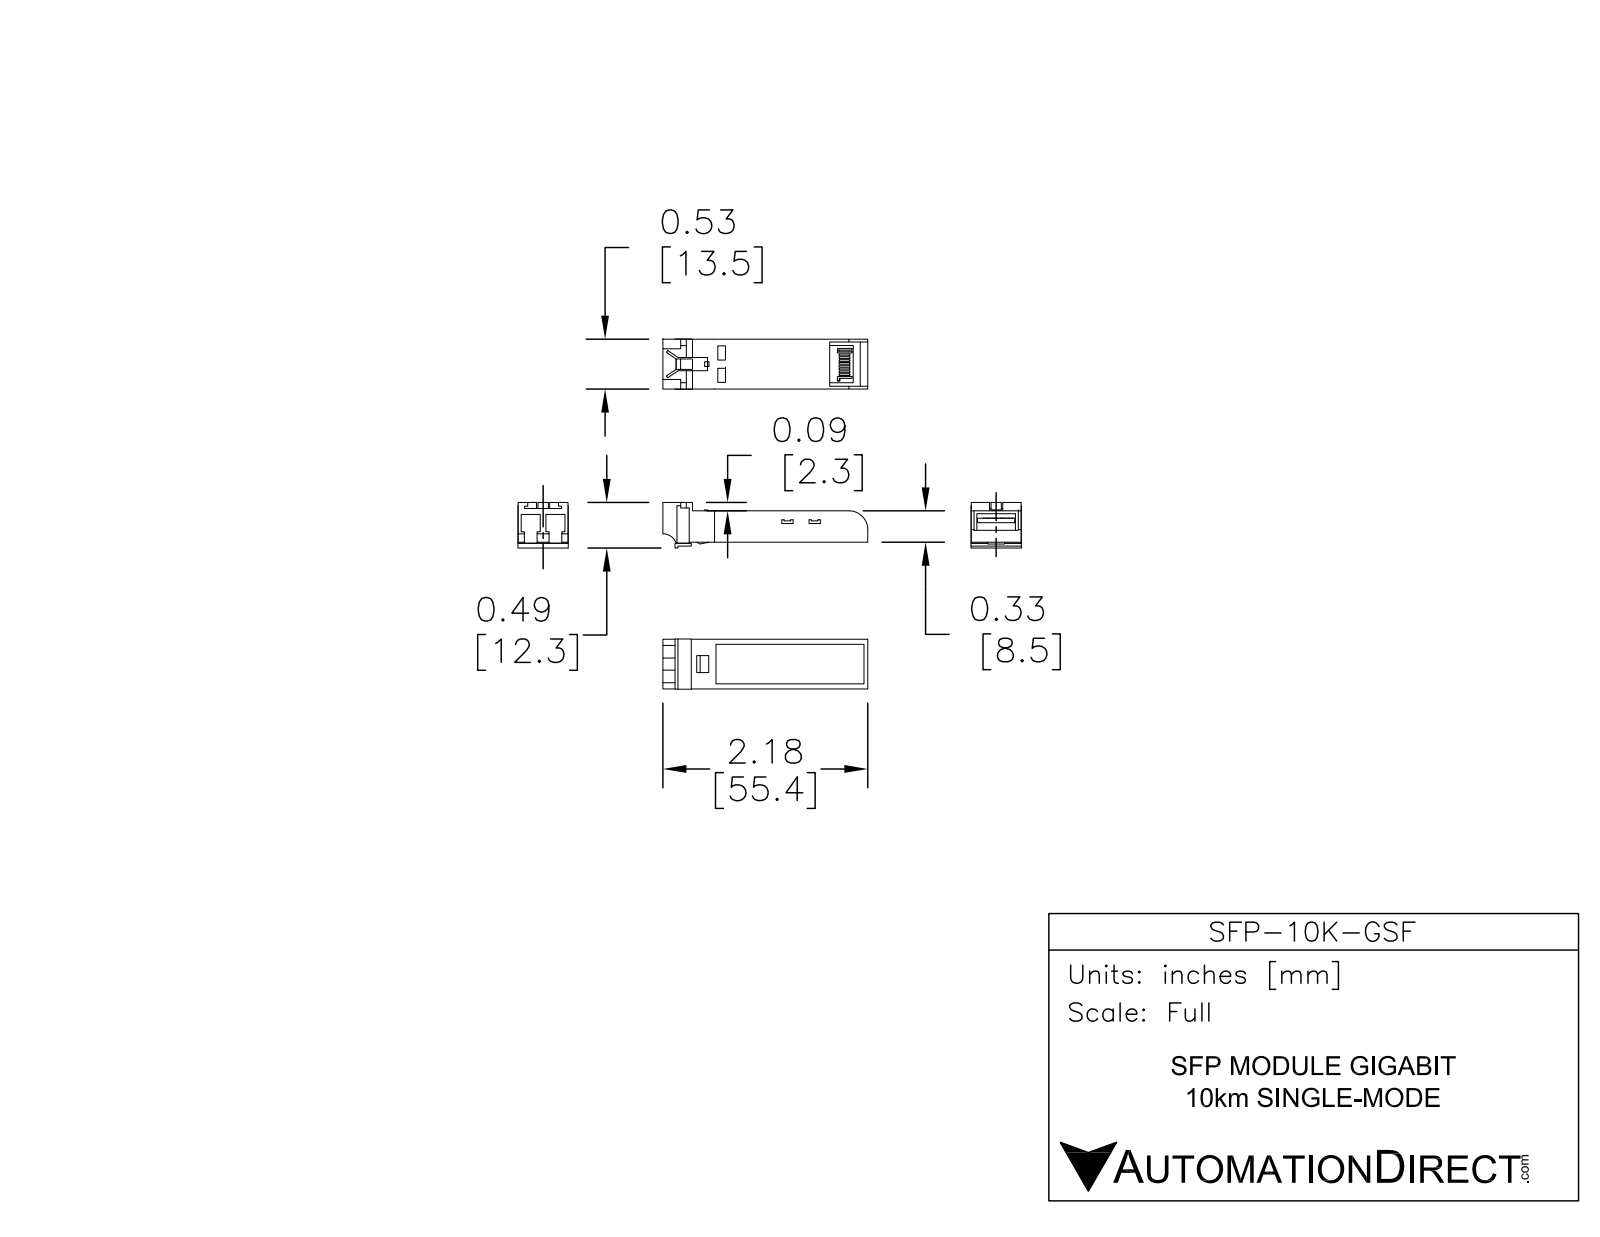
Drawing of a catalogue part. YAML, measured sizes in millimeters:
part_name: "SFP-10K-GSF"
step_written_by: "SolidWorks 2011 (AUTOMOTIVE_DESIGN)"
units: millimeters
bodies: {solids: 2, faces: 227, planar: 222, cylindrical: 5, other: 0}
overall_size: [55.4, 13.6, 12.3]
volume: 5060
surface_area: 3901
partial_cylinders:
  - {radius: 3.8, count: 1}
  - {radius: 5.1, count: 1}
face_to_face_distances: [13.5, 8.5, 0.8, 8.5, 12.7, 7.5, 0.9, 5.3, 6.5, 5.3]
